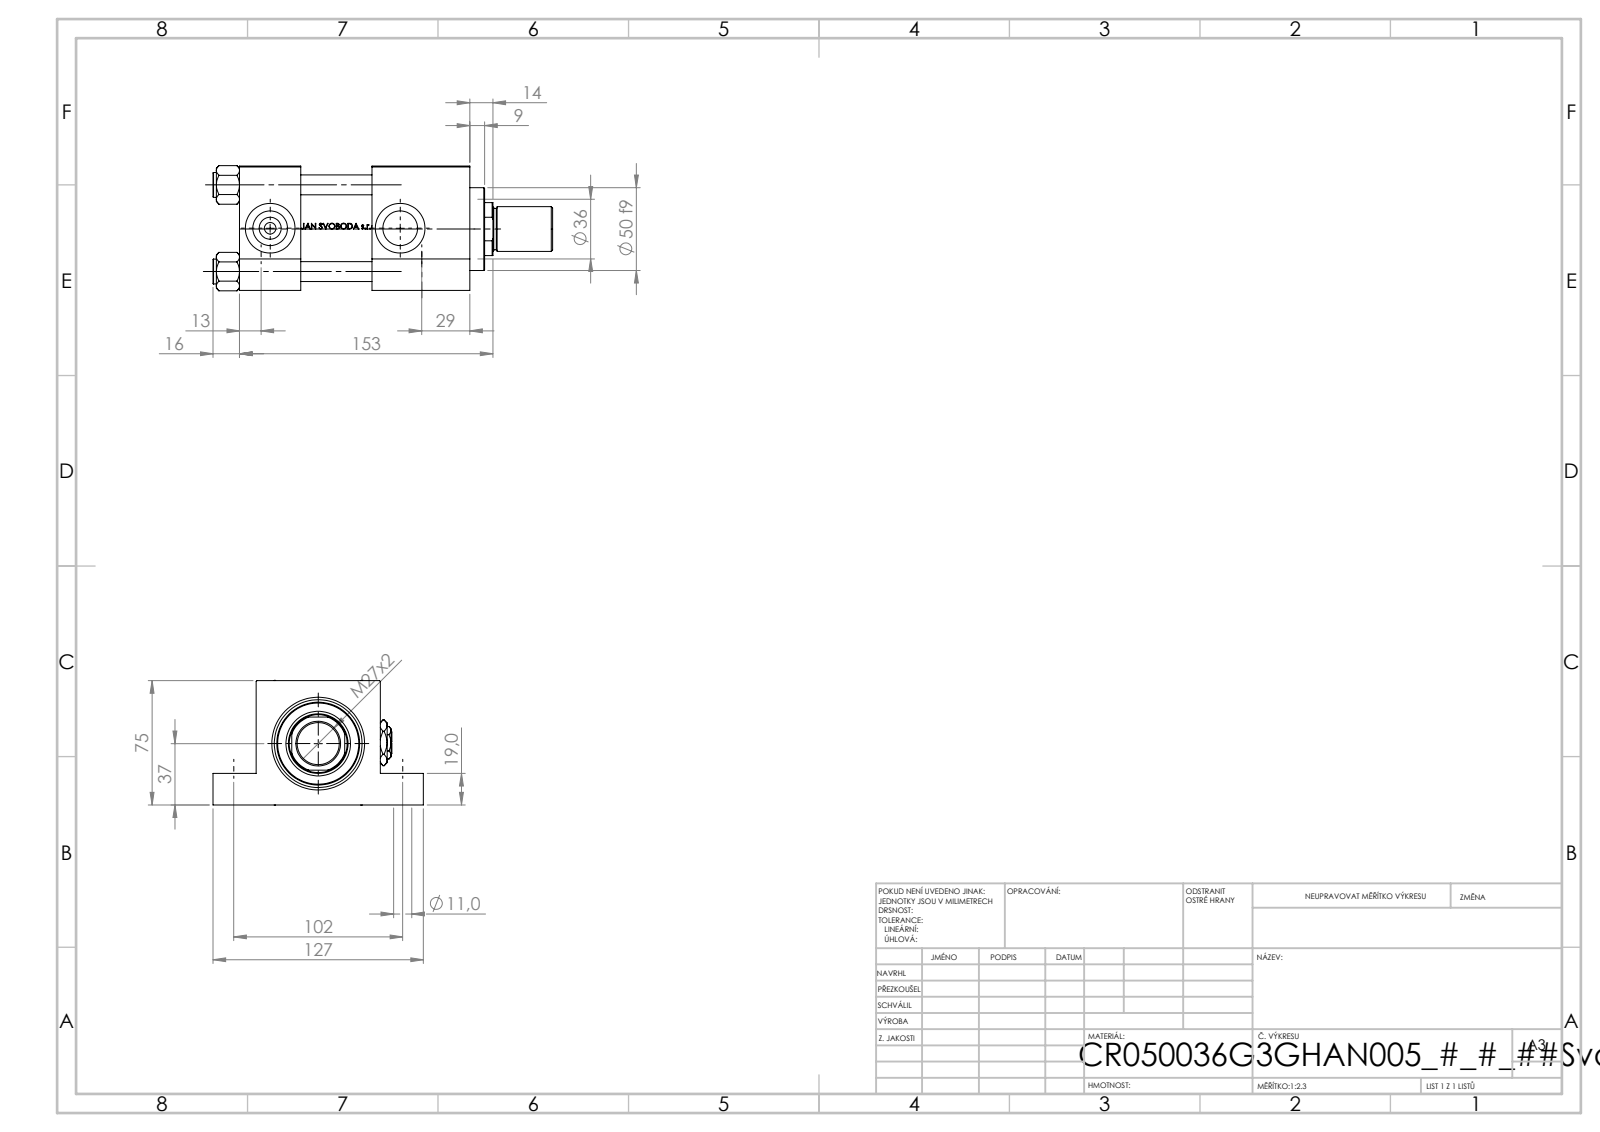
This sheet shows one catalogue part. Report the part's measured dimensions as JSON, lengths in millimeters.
{"part_name": "V215CR_G_Body; ROD_END_AH; NUT_M5_G; V215CR_G_TYCINKA (+3 more)", "step_written_by": "SolidWorks 2019 (CONFIG_CONTROL_DESIGN)", "units": "millimeters", "bodies": {"solids": 14, "faces": 1177, "planar": 481, "cylindrical": 132, "other": 564}, "overall_size": [205, 127, 75.54], "volume_mm3": 748574, "surface_area_mm2": 165710, "round_holes": [[11, 4], [12, 4], [7, 2], [20.96, 2], [30, 2], [25.5, 1], [36, 1], [39, 1], [41, 1], [53, 1]], "round_bosses_or_shafts": [[15, 4], [56, 1], [50, 1], [27, 1], [25, 1]], "partial_cylinders_radius": [[17.5, 1]], "face_to_face_distances": [75, 37, 56, 19, 80, 139, 102, 59, 43, 26], "hole_center_spacings": [52.3, 36.63, 37.34, 73.96, 97, 102, 140.76, 78.5]}
